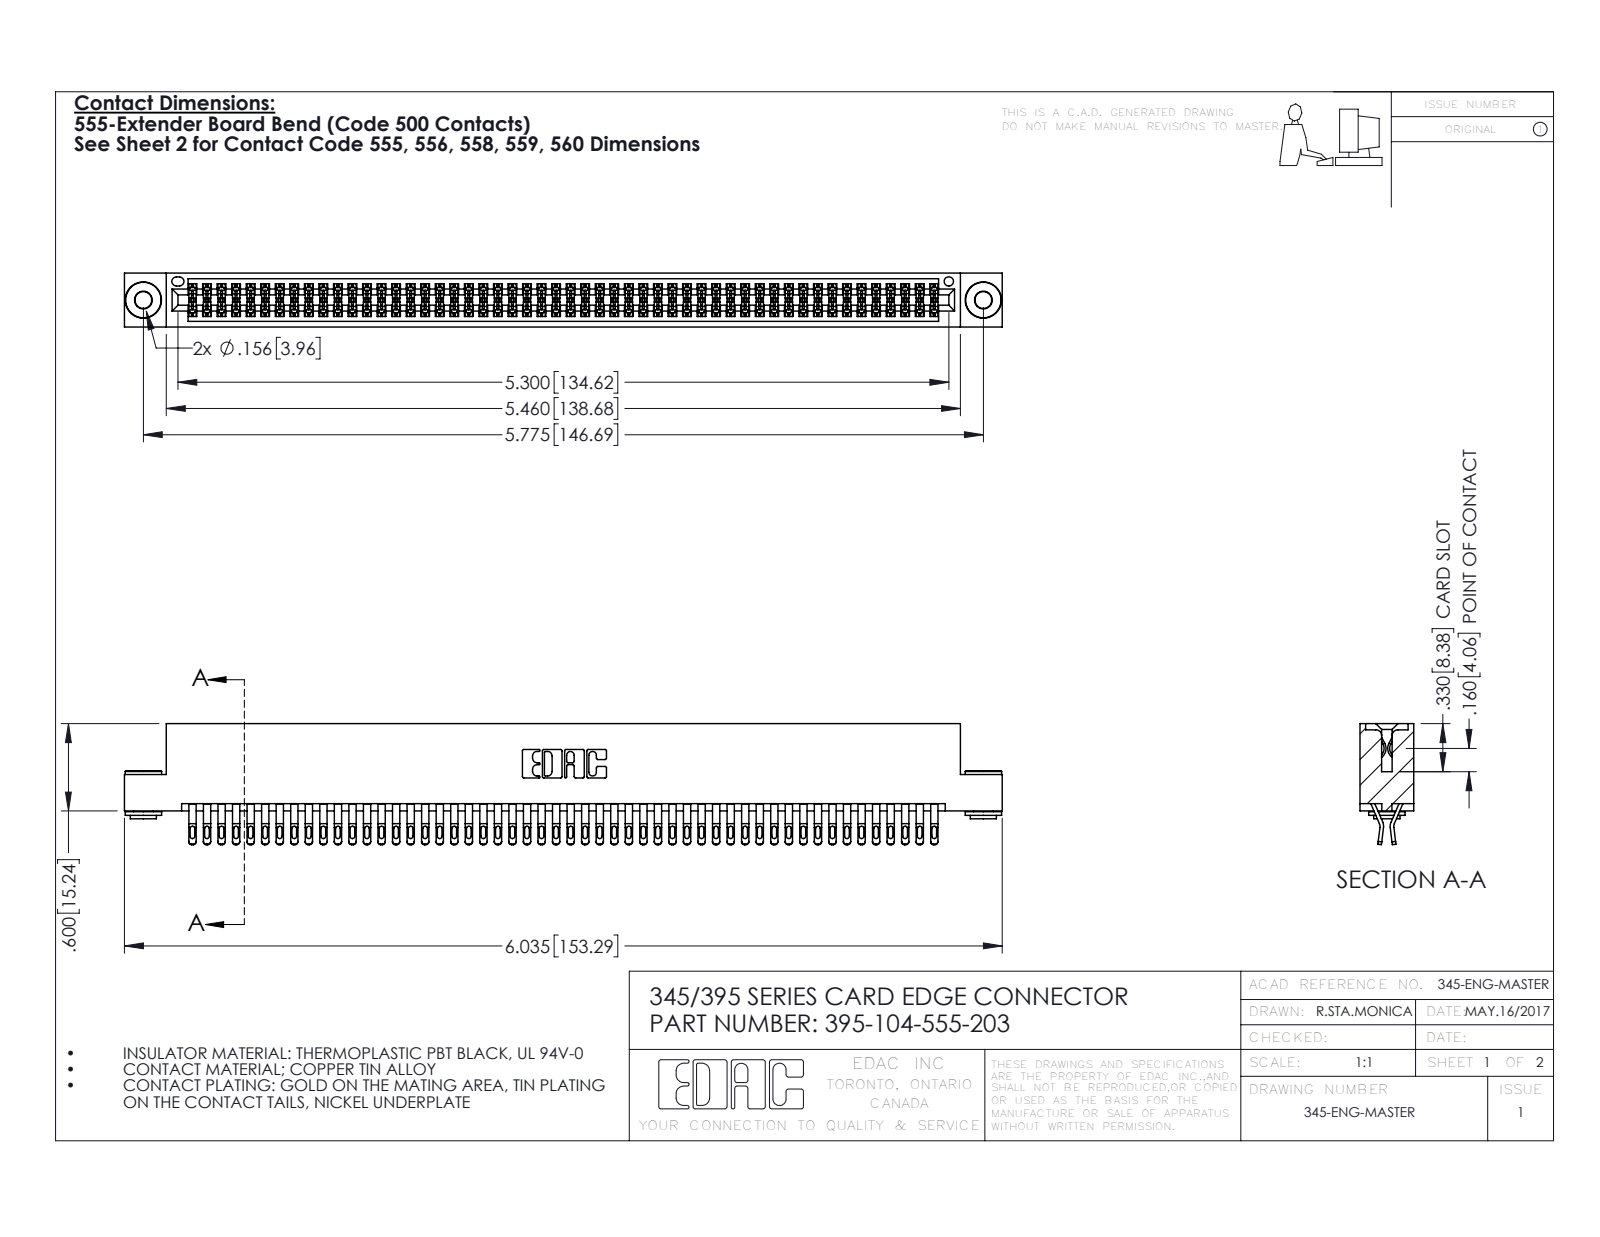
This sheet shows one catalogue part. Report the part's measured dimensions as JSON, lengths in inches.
{"part_name": "395-104-555-203; 345 Part_Flush Mounting Lugs - 0.156 Dia-TH; 345-250-002_345-250-002-102; 345-292-001_555 Tail", "step_written_by": "SolidWorks 2016 (CONFIG_CONTROL_DESIGN)", "units": "inches", "bodies": {"solids": 107, "faces": 5988, "planar": 3314, "cylindrical": 2666, "other": 8}, "overall_size": [6.035, 0.832, 0.37], "volume_in3": 0.934, "surface_area_in2": 37.31, "round_holes": [[0.116, 2], [0.156, 2], [0.064, 1]], "round_bosses_or_shafts": [[0.25, 2], [0.18, 2], [0.136, 2]], "partial_cylinders_radius": [[0.016, 260], [0.02, 208], [0.006, 156], [0.01, 22], [0.007, 6], [0.031, 6], [0.026, 3], [0.01, 2]], "face_to_face_distances": [0.072, 0.298, 0.025, 0.2, 0.37, 0.098, 0.272, 0.225, 0.175, 0.149], "hole_center_spacings": [0.27, 5.539, 5.775]}
